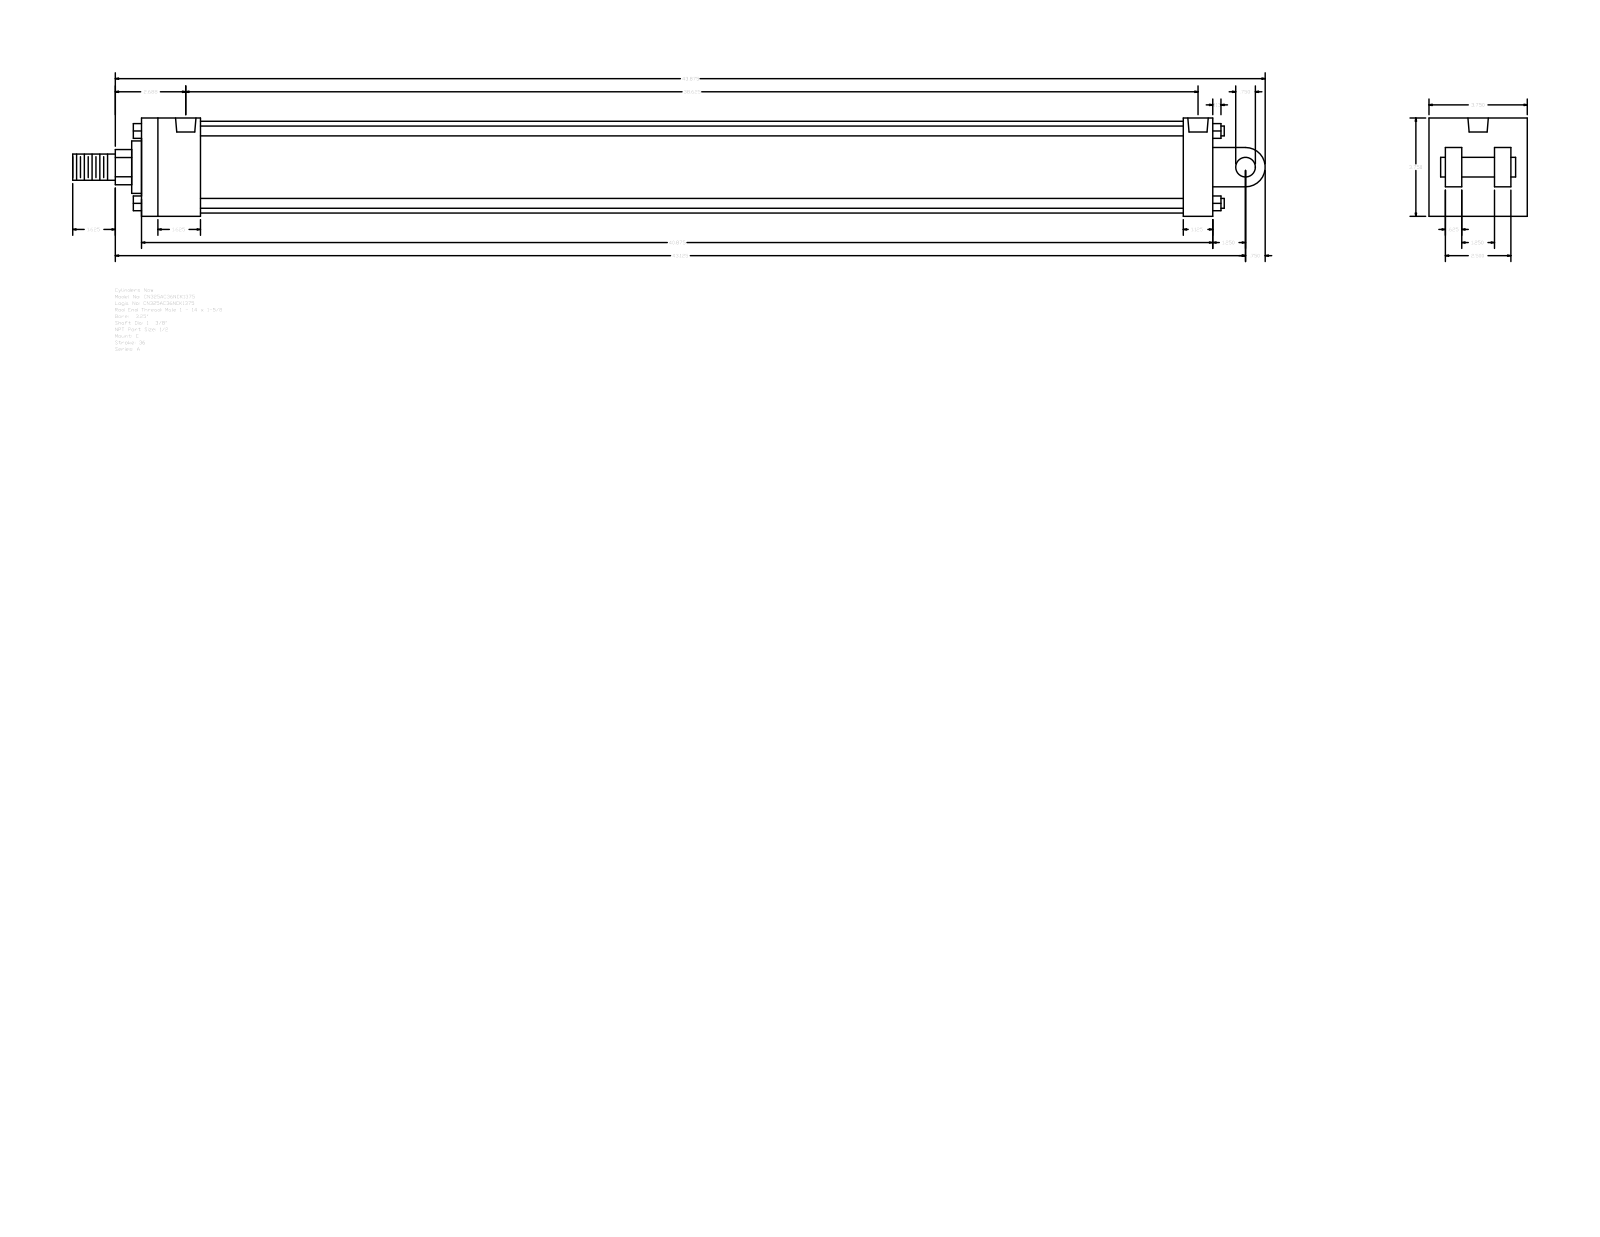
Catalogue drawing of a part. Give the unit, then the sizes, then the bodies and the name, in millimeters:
Units: millimetres
Overall size (bounding box): 1155.7 × 95.25 × 95.25
Round holes (diameter × count): ⌀8.73 ×4, ⌀19.77 ×2
Round bosses / shafts (diameter × count): ⌀9.53 ×4, ⌀88.9 ×1, ⌀50.8 ×1, ⌀34.92 ×1, ⌀25.4 ×1, ⌀19.05 ×1
Partial cylindrical surfaces — rounded edges, fillets, slot ends (radius × count): R17.06 ×1, R19.05 ×1
Main face-to-face distances: 95.24, 1038.22, 15.87, 28.57, 63.5, 66.67, 57.15, 31.74, 79.37, 47.63
Hole centre spacings: 3.18, 974.72, 977.9, 981.08
Bodies: 0 solids, 135 faces (102 planar, 33 cylindrical, 0 other)
Part name (STEP PRODUCT): A_C__0325_1.375
STEP written by: GSSL Pune (CONFIG_CONTROL_DESIGN)
